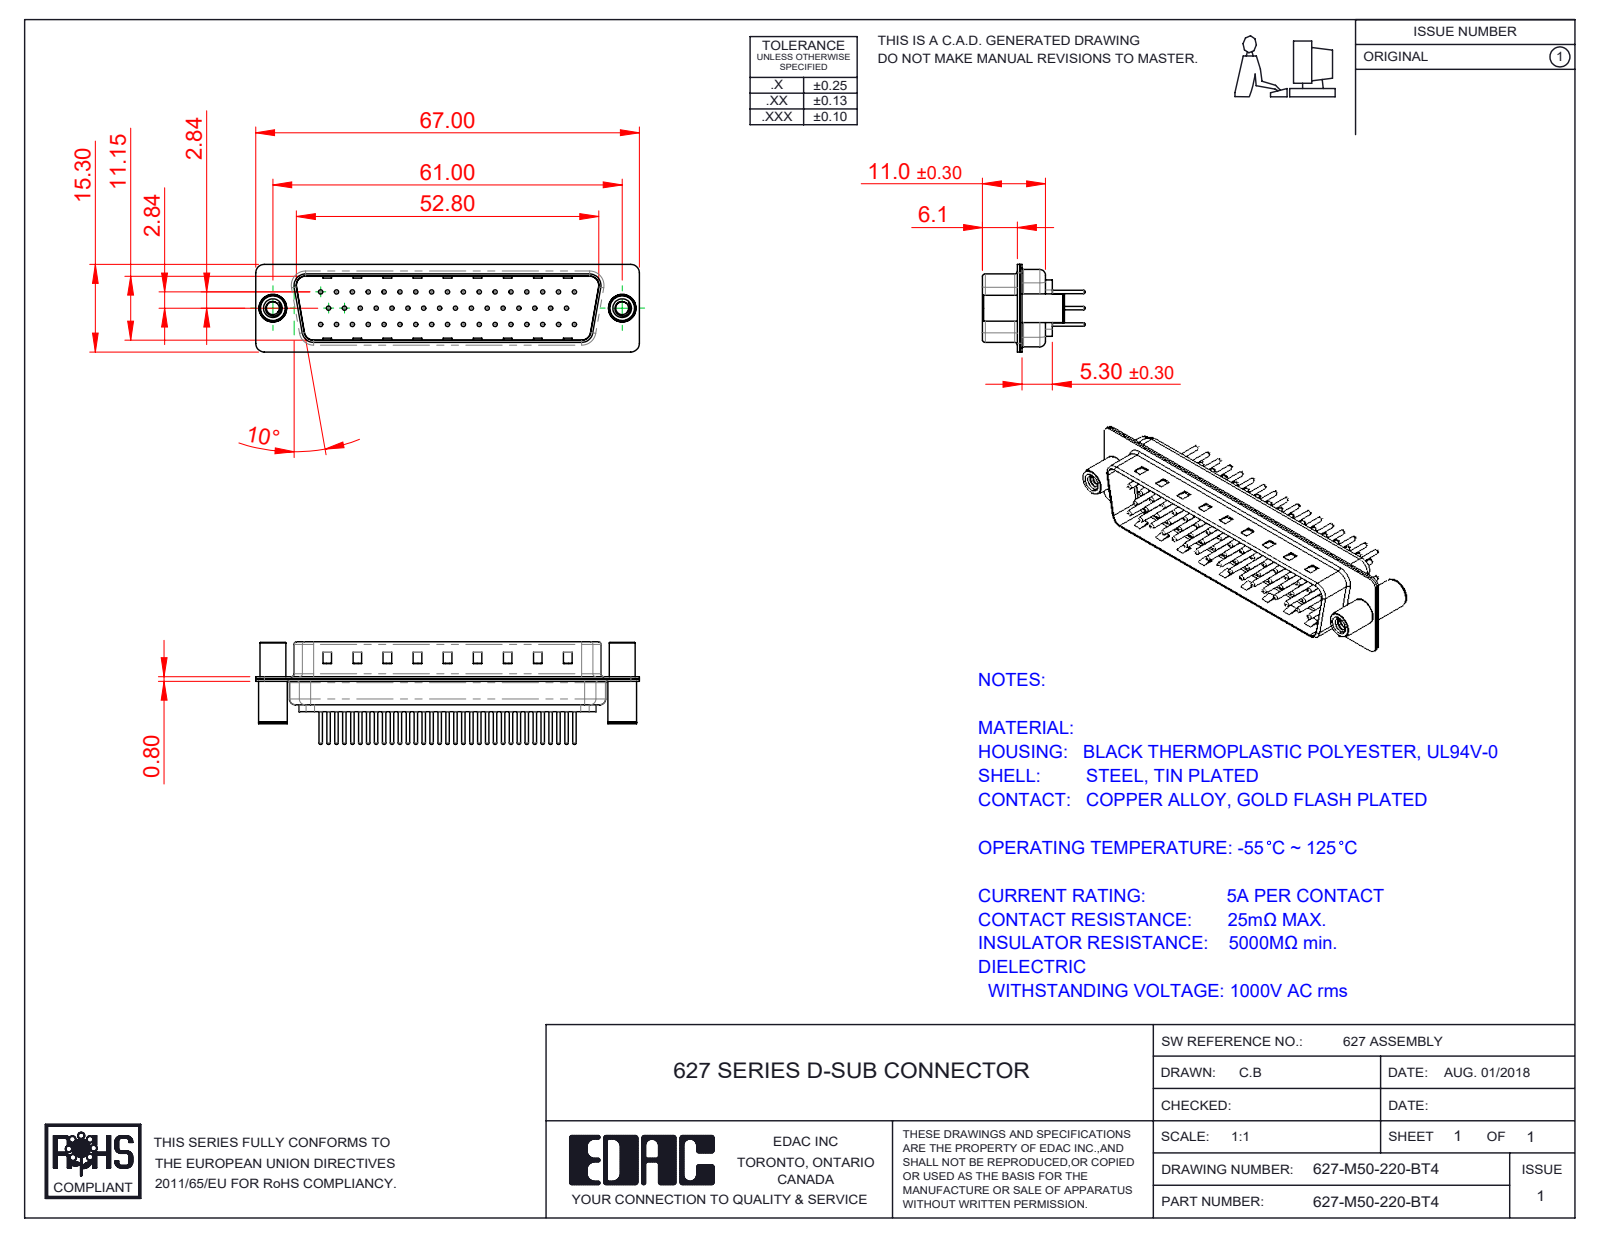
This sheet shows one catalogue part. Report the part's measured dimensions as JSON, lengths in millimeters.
{"part_name": "627M Shell Front_50 Contacts; 627M Contact Row 3_20; 627-M50-220-BT4; 627M Contact Row 1_20 (+4 more)", "step_written_by": "SolidWorks 2020 (CONFIG_CONTROL_DESIGN)", "units": "millimeters", "bodies": {"solids": 55, "faces": 2348, "planar": 559, "cylindrical": 893, "other": 896}, "overall_size": [67, 17.9, 15.3], "volume_mm3": 4812, "surface_area_mm2": 11228, "round_holes": [[0.75, 50], [1.6, 50], [2, 50], [2.26, 2], [3.26, 2], [4, 2], [4.8, 2]], "round_bosses_or_shafts": [[1.5, 50], [0.6, 50], [5, 2], [4.9, 2], [4.5, 2]], "partial_cylinders_radius": [[1.5, 16], [2, 12], [0.5, 8], [1.6, 8], [0.25, 4], [0.6, 4], [0.65, 4], [0.9, 4]], "face_to_face_distances": [0.4, 11.55, 5.7, 6.1, 0.78, 0.77, 12.33, 5.3, 12.32, 13.1], "hole_center_spacings": [3.16, 2.77, 5.54, 8.31, 11.08, 13.85, 16.62, 5.03]}
